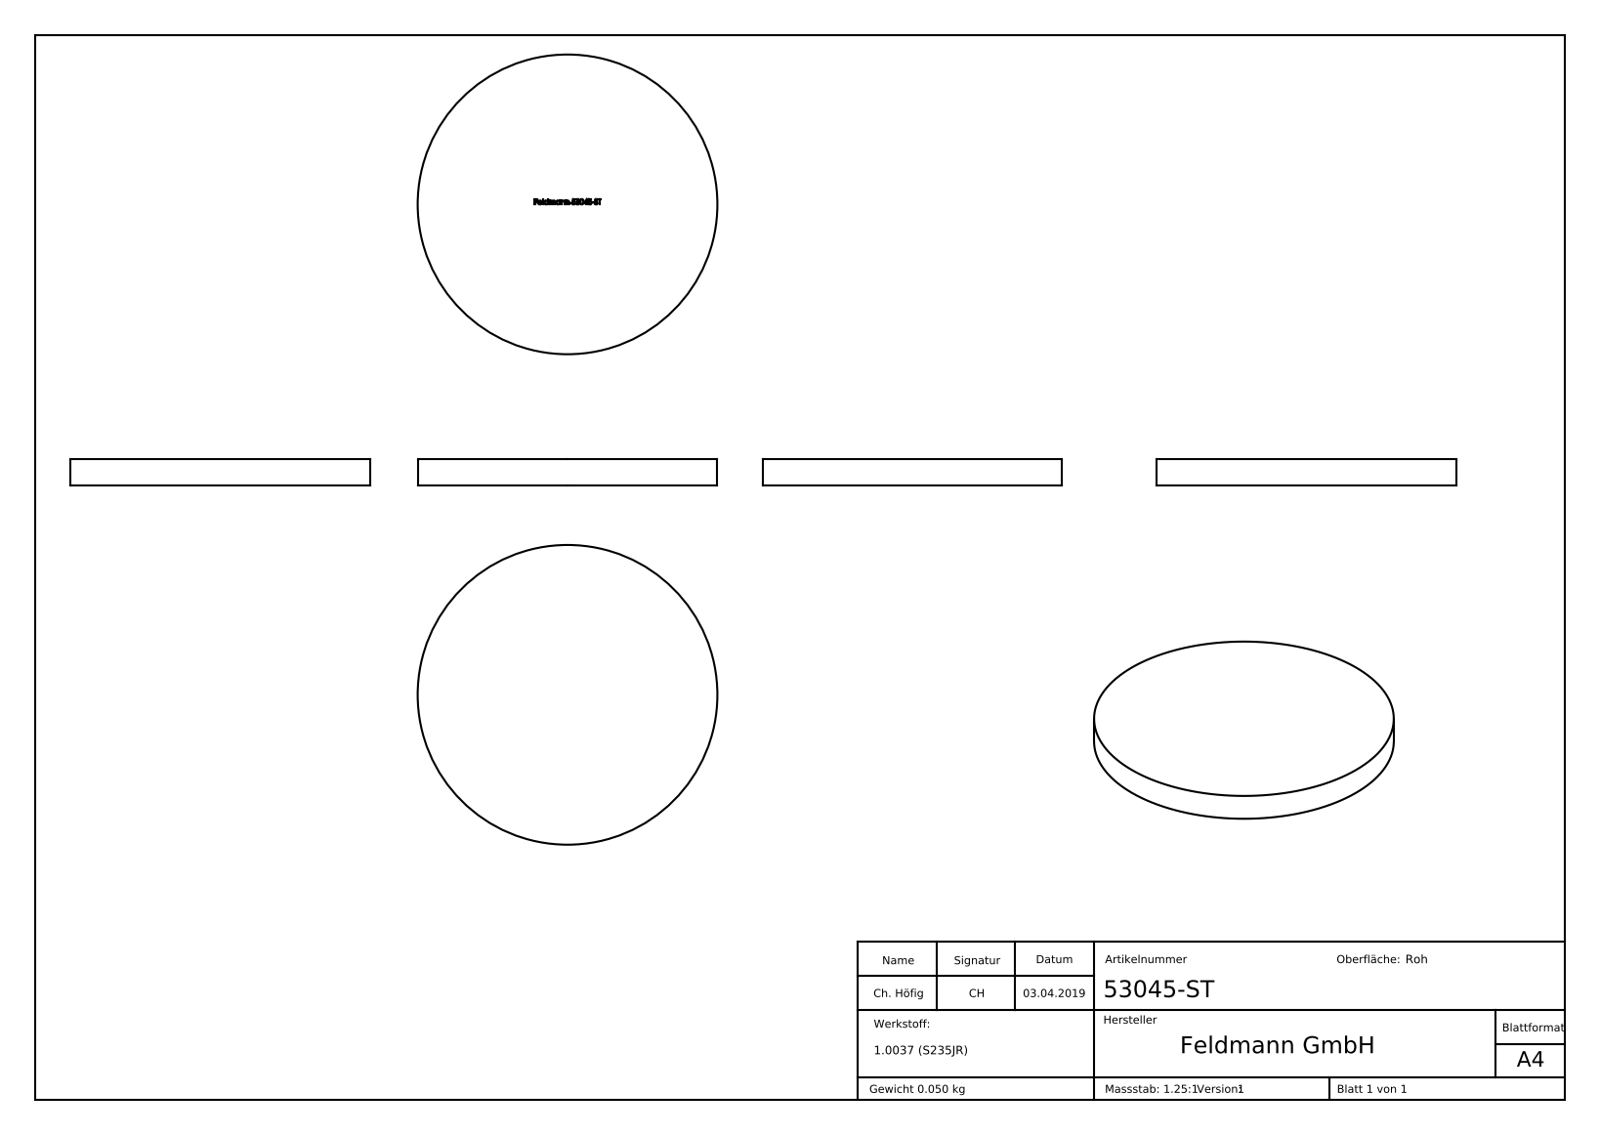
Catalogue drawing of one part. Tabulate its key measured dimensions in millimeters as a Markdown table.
| quantity | value |
| --- | --- |
| part name | 53045-ST |
| STEP written by | SolidWorks 2015 (CONFIG_CONTROL_DESIGN) |
| units | millimeters |
| bodies | 1 solid, 223 faces (119 planar, 2 cylindrical, 102 other) |
| overall size | 45 × 45 × 4 |
| volume | 6 362 mm³ |
| surface area | 3 752 mm² |
| round bosses / shafts (diameter × count) | 45 × 1 |
| main face-to-face distances | 4, 3.9, 0.44, 0.79, 0.99, 1.78, 1.21, 8.49, 9.7, 0.75 |
